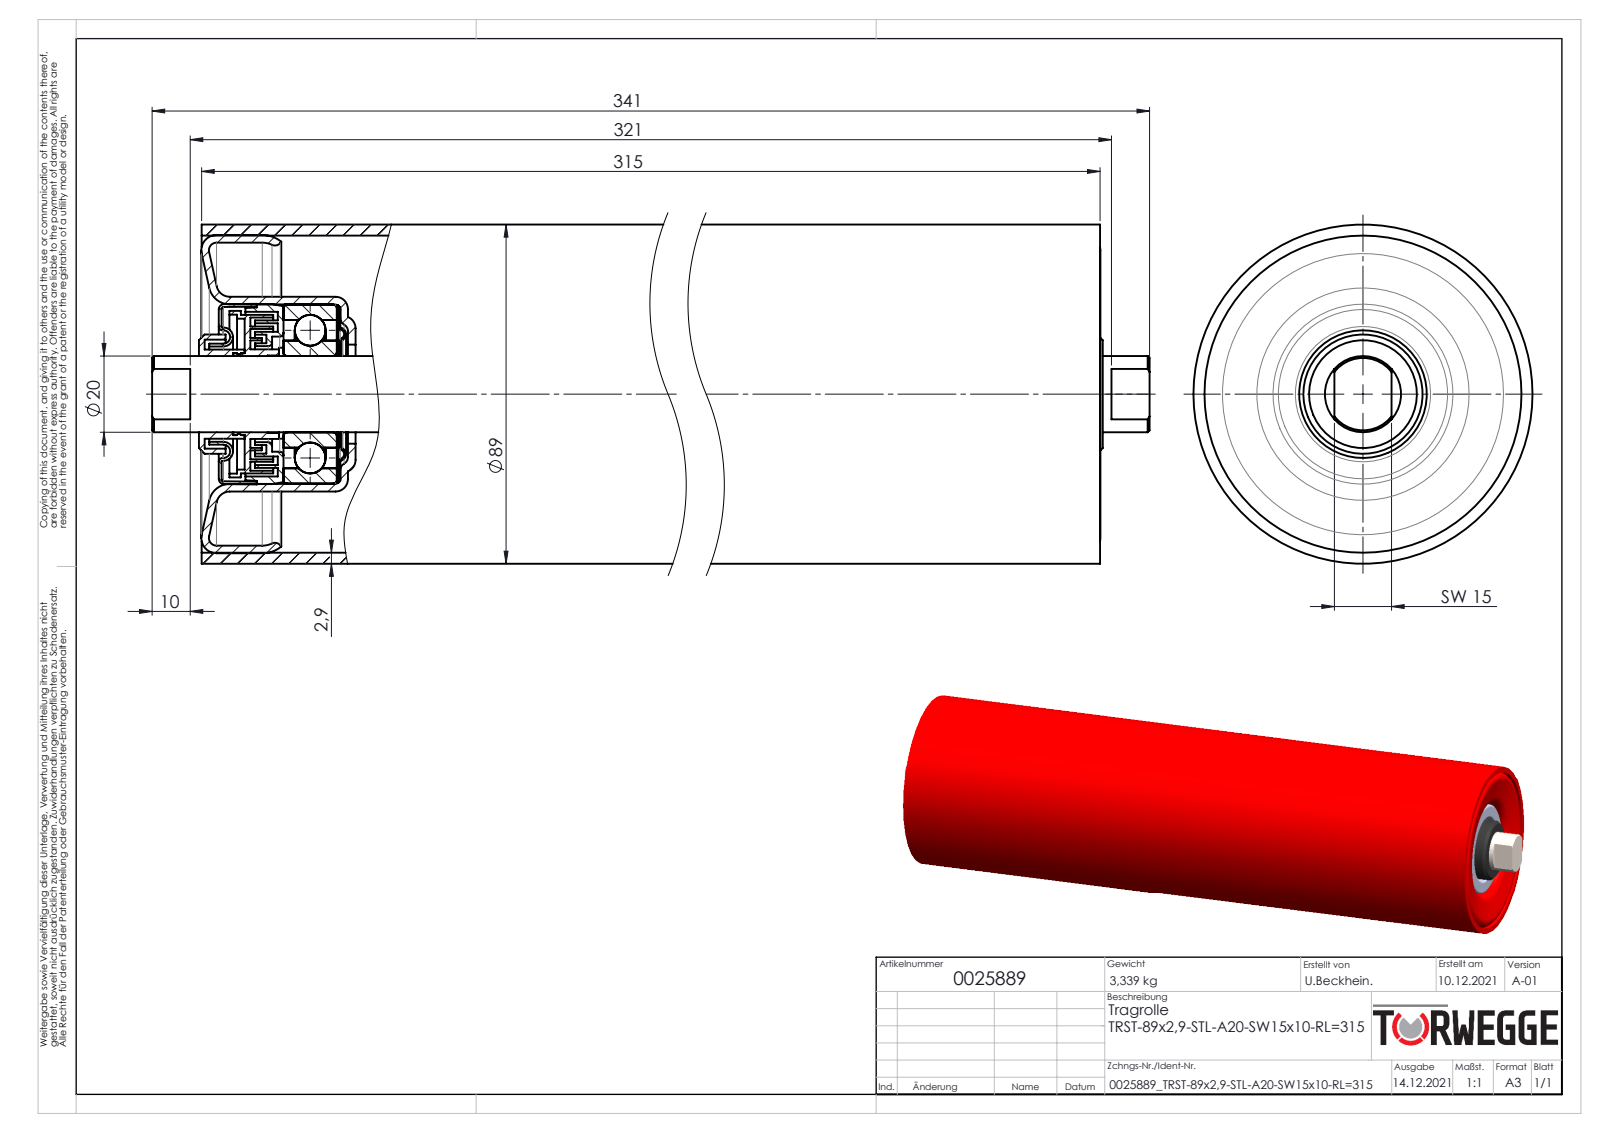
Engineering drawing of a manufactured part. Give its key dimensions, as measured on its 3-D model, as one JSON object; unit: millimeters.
{"part_name": "0025889", "step_written_by": "SolidWorks 2020 (AUTOMOTIVE_DESIGN)", "units": "millimeters", "bodies": {"solids": 24, "faces": 606, "planar": 114, "cylindrical": 244, "other": 248}, "overall_size": [341, 89, 89], "volume_mm3": 506058, "surface_area_mm2": 348777, "round_holes": [[2, 4], [19, 1], [19.6, 1], [20, 1], [20.3, 1], [21, 1], [21.5, 1], [25, 1], [25.2, 1], [26, 1], [28.2, 1], [28.6, 1]], "round_bosses_or_shafts": [[23.9, 2], [89, 1], [83.5, 1], [51.1, 1], [47.2, 1], [47, 1], [46.5, 1], [43.7, 1]], "partial_cylinders_radius": [[2, 8], [13.5, 1]], "face_to_face_distances": [14, 258.02, 14.92, 257.1, 0.92, 243.1, 272.02, 10.2, 24.2, 25.12], "hole_center_spacings": [11.49, 11.5, 22.55, 3.99, 4, 21.43, 22.99]}
